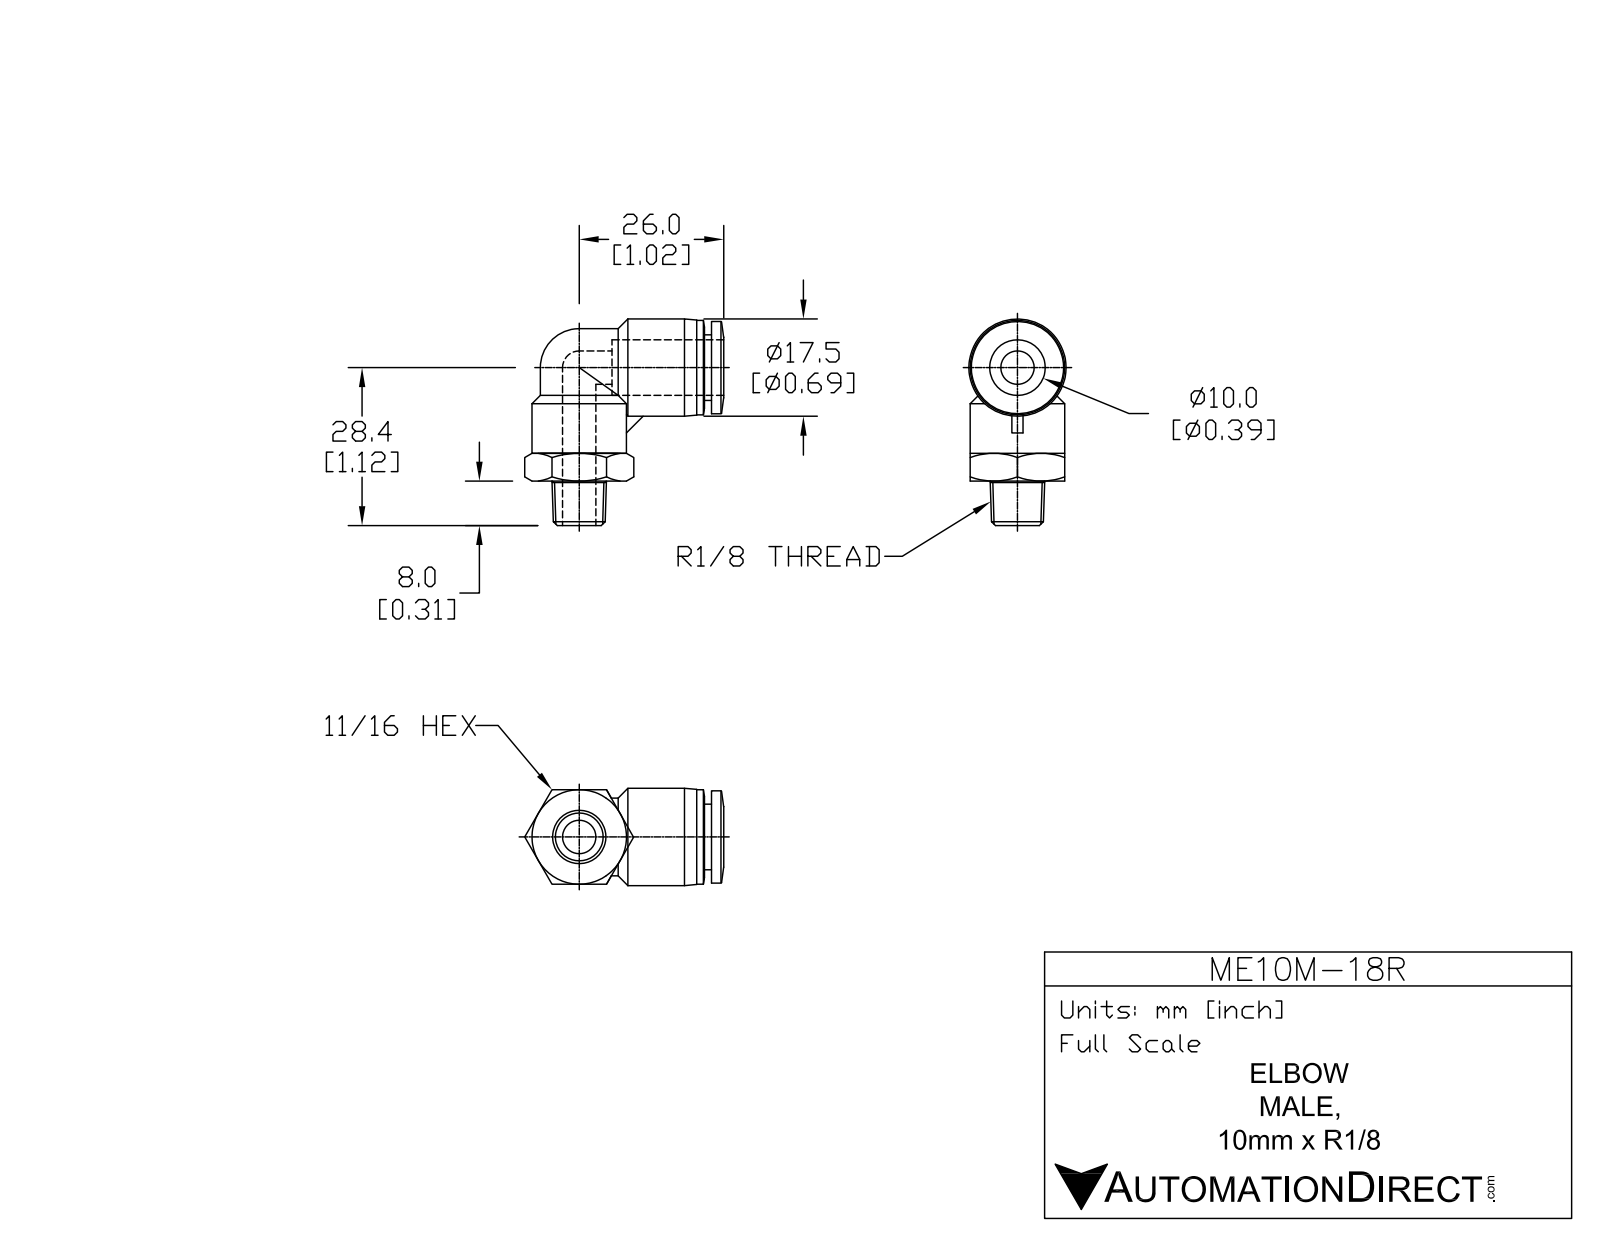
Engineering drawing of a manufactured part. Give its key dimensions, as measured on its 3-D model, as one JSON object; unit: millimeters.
{"part_name": "ME10M-18R", "step_written_by": "SolidWorks 2015 (AUTOMOTIVE_DESIGN)", "units": "millimeters", "bodies": {"solids": 1, "faces": 71, "planar": 16, "cylindrical": 20, "other": 35}, "overall_size": [37.3, 34.4, 17.5], "volume_mm3": 7140, "surface_area_mm2": 4386, "round_holes": [[6, 2], [10.3, 1]], "round_bosses_or_shafts": [[17, 2], [17.5, 1], [16.6, 1], [14, 1], [11.8, 1]], "partial_cylinders_radius": [[7, 1]], "face_to_face_distances": [17, 1.2, 16.7, 18, 8, 7.5, 9.5, 2, 15.3, 1.4]}
